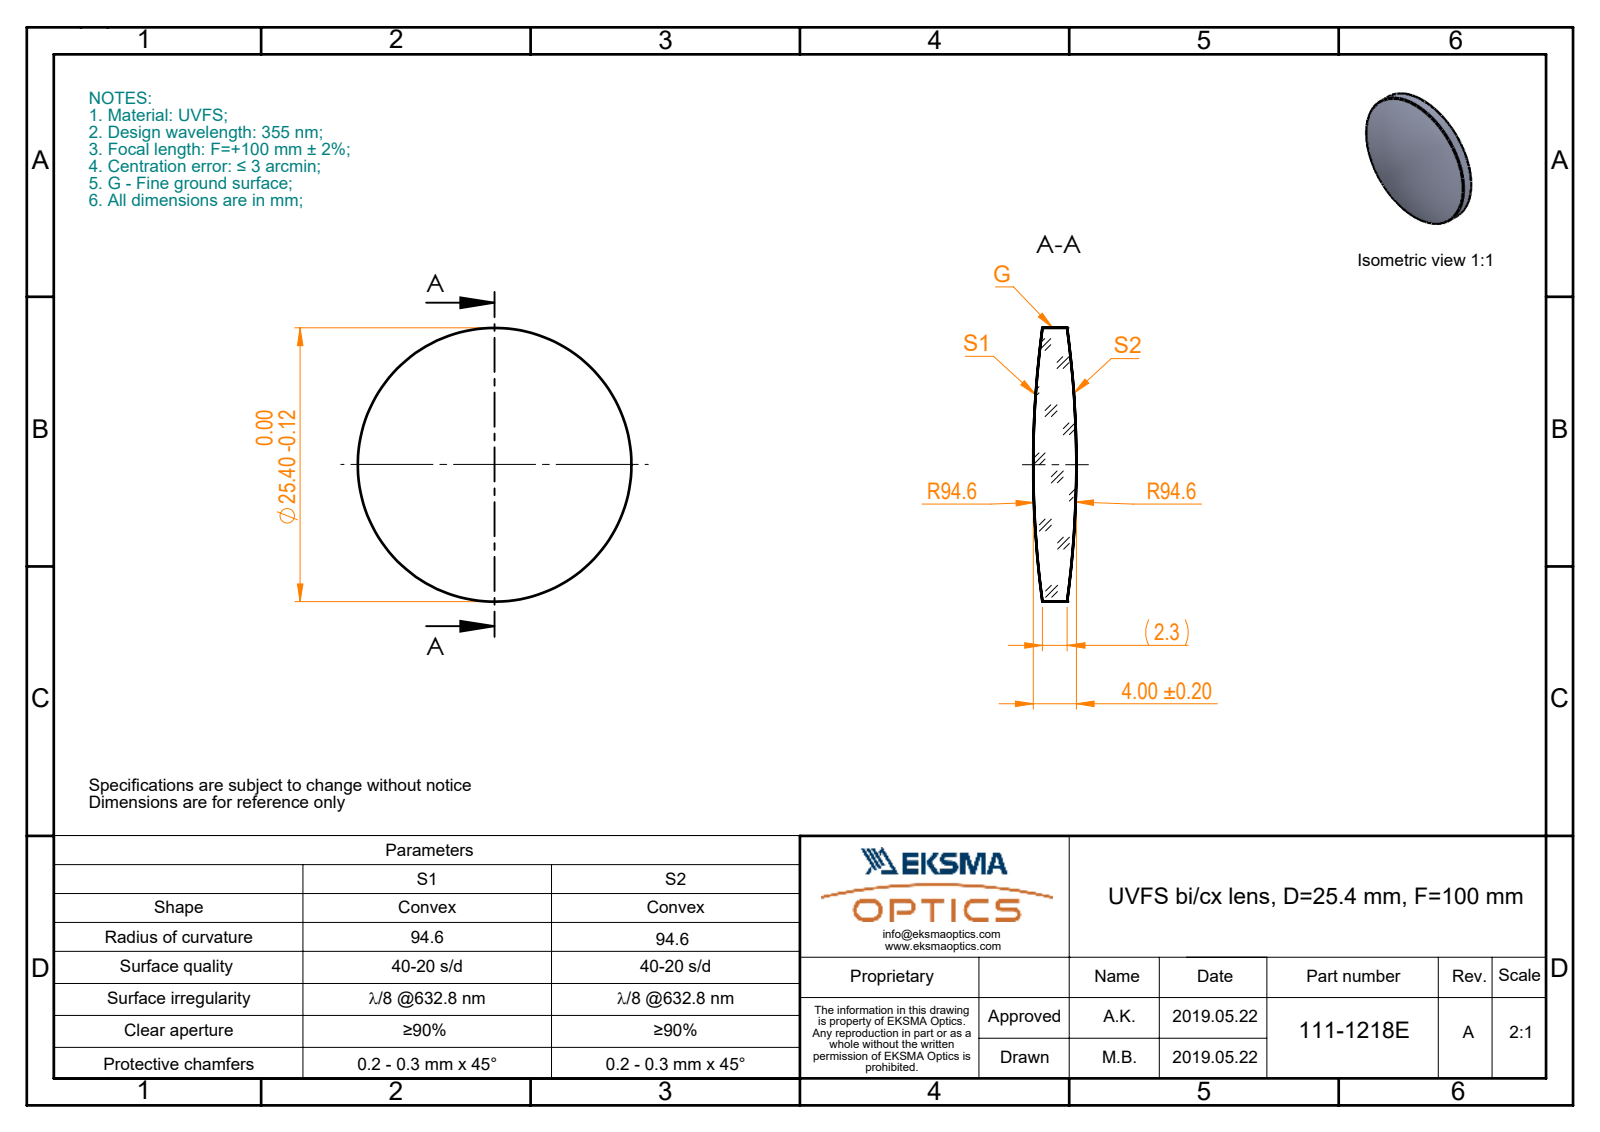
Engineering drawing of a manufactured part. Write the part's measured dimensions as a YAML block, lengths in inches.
part_name: "111-1218E UVFS bi-cx 25.4 F100"
step_written_by: "SolidWorks 2017 (CONFIG_CONTROL_DESIGN)"
units: inches
bodies: {solids: 1, faces: 6, planar: 0, cylindrical: 2, other: 4}
overall_size: [1, 1, 0.157]
volume: 0.097
surface_area: 1.86
round_bosses_or_shafts:
  - {diameter: 1, count: 1}
